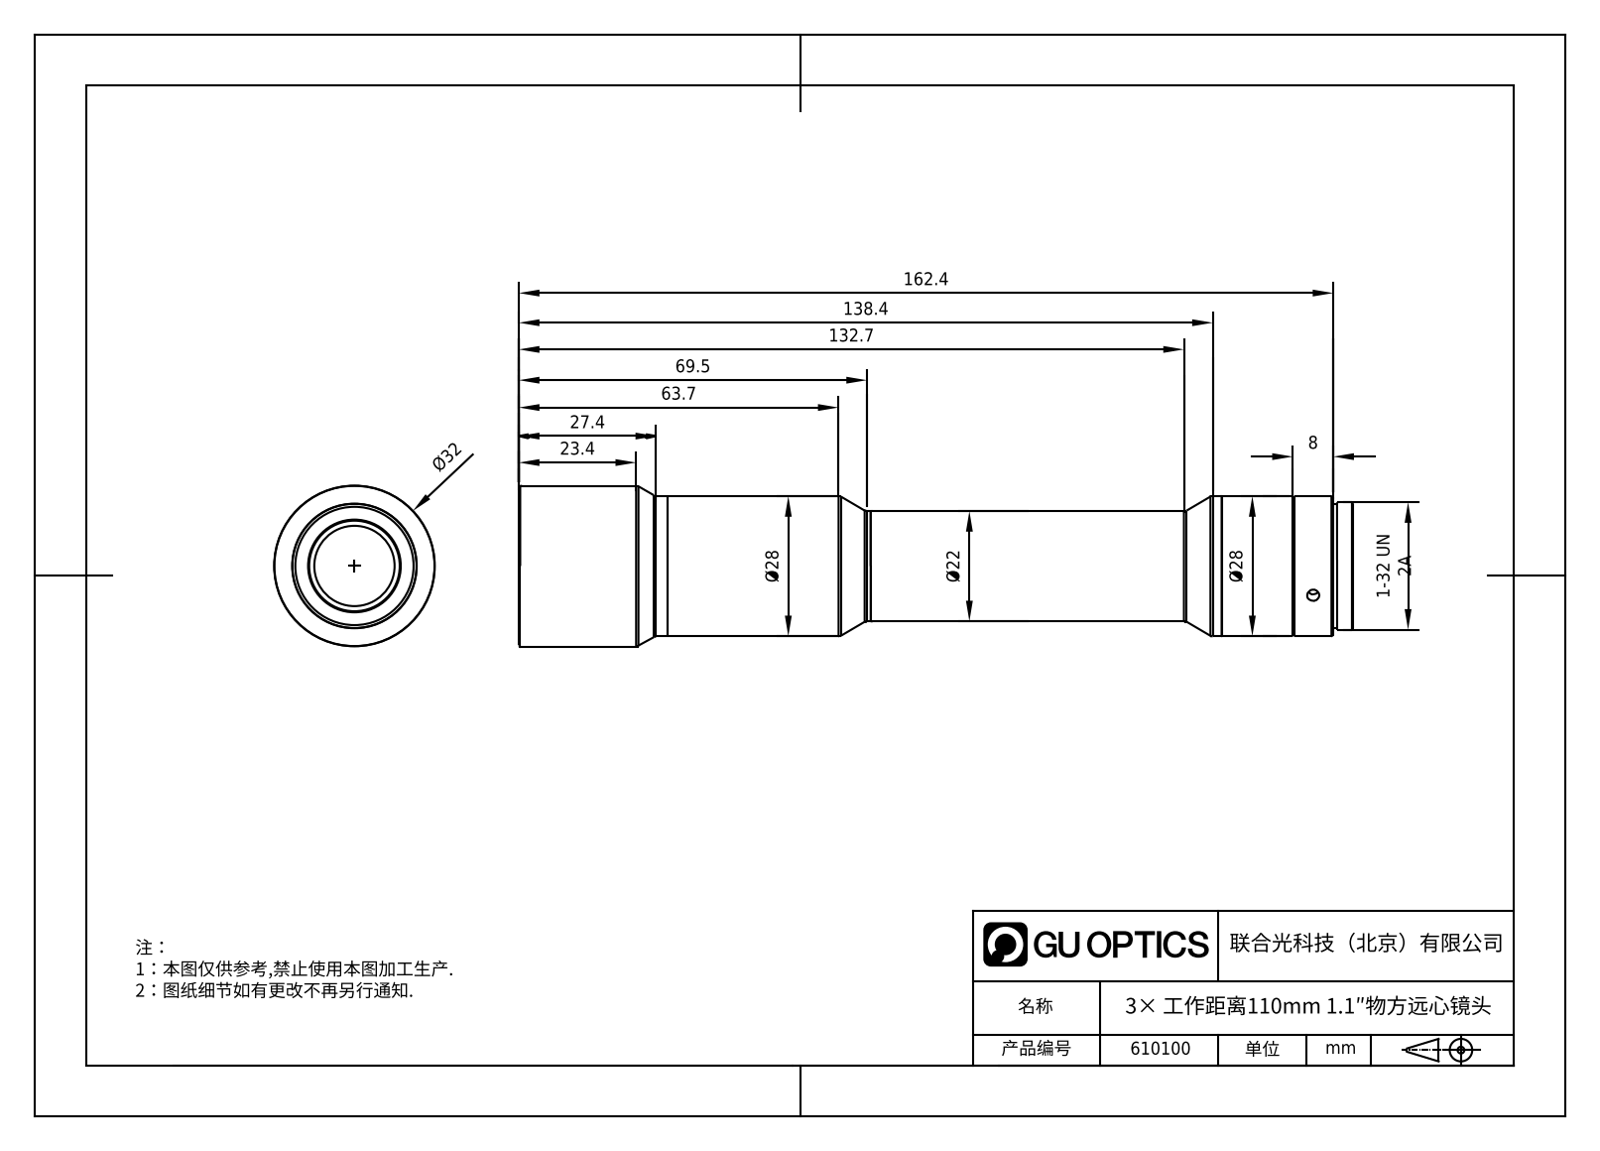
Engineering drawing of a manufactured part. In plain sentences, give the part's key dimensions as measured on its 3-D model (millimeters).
The part is named "WWK40-108-111V3". Its 3-D file was written by "SolidWorks 2017 (CONFIG_CONTROL_DESIGN)". It is 1 solid with 62 faces: 7 planar, 27 cylindrical and 28 other. Overall it measures 166.42 by 32 by 32 millimeters. Its volume is 88 115 cubic millimeters and its surface area 15 642 square millimeters. Round holes: 3 of diameter 2.4, 1 of diameter 22, 1 of diameter 29.5. Round bosses or shafts: 1 of diameter 32, 1 of diameter 28, 1 of diameter 25.4, 1 of diameter 24.6. Partial cylindrical surfaces (rounded edges, fillets, slot ends): 1 of radius 11.87. The main face-to-face distances are 162.46, 159.67, 2.79, 163.67, 4, 1.21, 2.75, 162.42, 165.21, 166.42.
